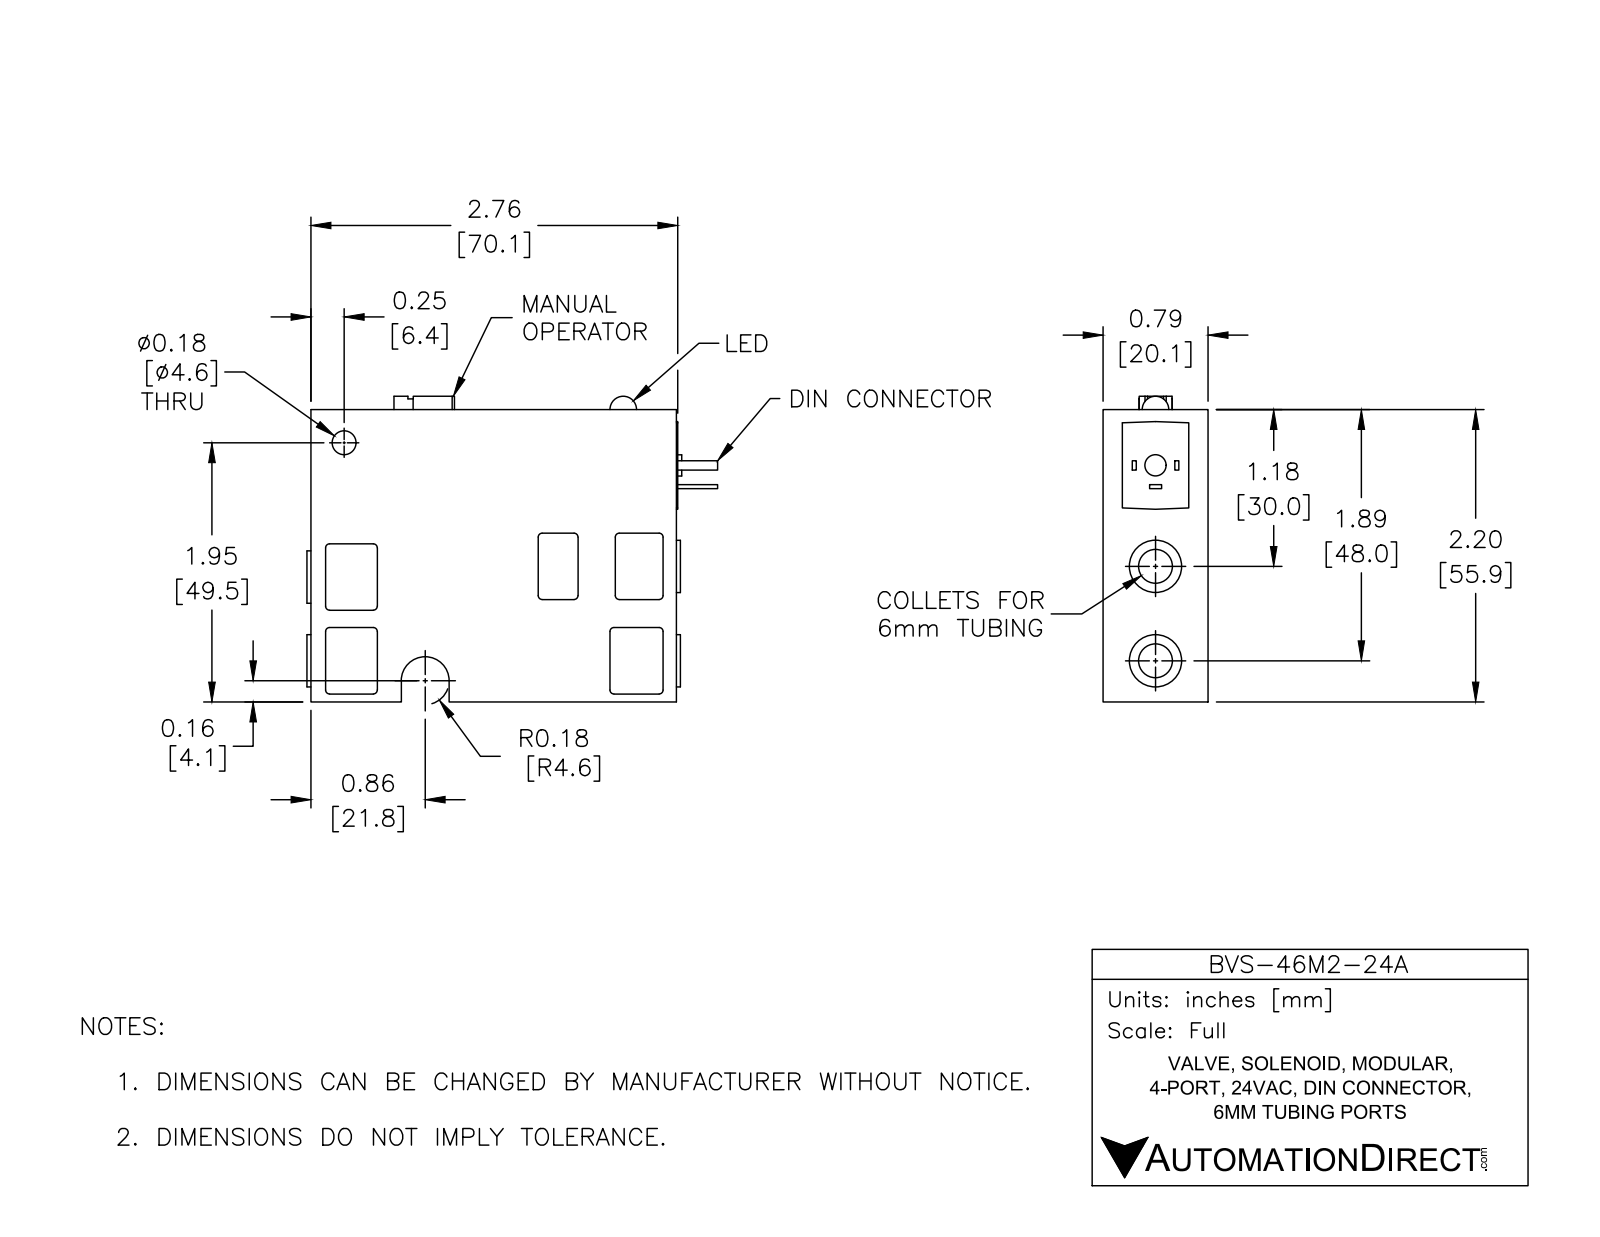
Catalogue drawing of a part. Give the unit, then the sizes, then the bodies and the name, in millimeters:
Units: millimetres
Overall size (bounding box): 78.5 × 58.4 × 20.1
Round holes (diameter × count): ⌀6.5 ×3, ⌀2.5 ×1, ⌀4.6 ×1
Round bosses / shafts (diameter × count): ⌀10 ×3, ⌀4.1 ×1
Partial cylindrical surfaces — rounded edges, fillets, slot ends (radius × count): R0.8 ×20, R0.5 ×2, R3.2 ×1, R4.6 ×1
Main face-to-face distances: 20.1, 2.5, 55.9, 17.5, 69.9, 15, 12.7, 2.8, 67.3, 0.8
Hole centre spacings: 2, 14, 16, 16, 18, 32
Volume: 71 680 mm³ · Surface area: 16 250 mm²
Bodies: 1 solid, 169 faces (99 planar, 68 cylindrical, 2 other)
Part name (STEP PRODUCT): BVS-46M2-24A
STEP written by: SolidWorks 2016 (AUTOMOTIVE_DESIGN)
